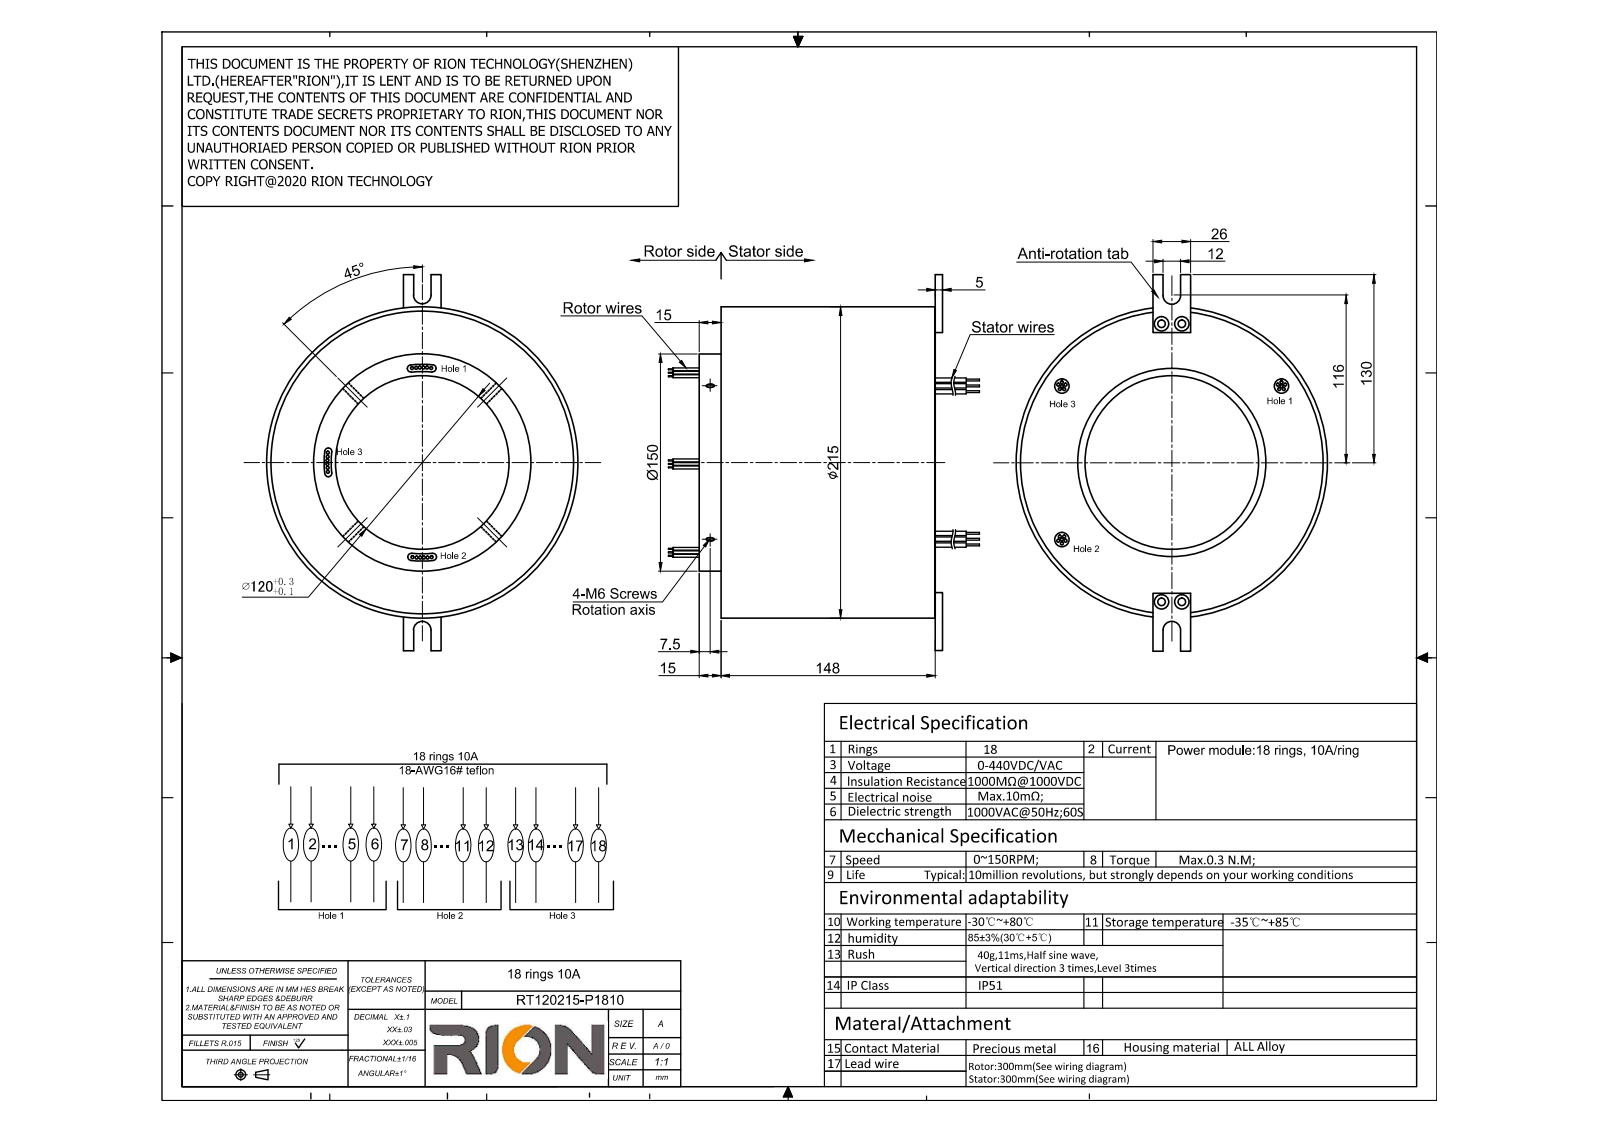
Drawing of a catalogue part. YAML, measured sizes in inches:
part_name: "RT120215-P1810"
step_written_by: "SolidWorks 2014 (CONFIG_CONTROL_DESIGN)"
units: inches
bodies: {solids: 1, faces: 230, planar: 76, cylindrical: 138, other: 16}
overall_size: [10.236, 9.843, 8.465]
volume: 232.2
surface_area: 385.9
round_holes:
  - {diameter: 0.197, count: 8}
  - {diameter: 0.165, count: 4}
  - {diameter: 0.394, count: 3}
  - {diameter: 4.724, count: 1}
  - {diameter: 5.126, count: 1}
  - {diameter: 8.236, count: 1}
round_bosses_or_shafts:
  - {diameter: 0.083, count: 36}
  - {diameter: 8.465, count: 1}
  - {diameter: 8.228, count: 1}
  - {diameter: 5.906, count: 1}
  - {diameter: 5.118, count: 1}
partial_cylinders:
  - {radius: 0.098, count: 6}
  - {radius: 0.236, count: 2}
  - {radius: 2.48, count: 1}
  - {radius: 2.677, count: 1}
face_to_face_distances: [5.827, 0.591, 6.417, 0.197, 6.614, 6.024, 0.276, 1.024, 0.748, 0.039]
hole_center_spacings: [3.789, 3.192, 3.642, 3.671, 6.463, 6.713, 0.551, 7.559]
